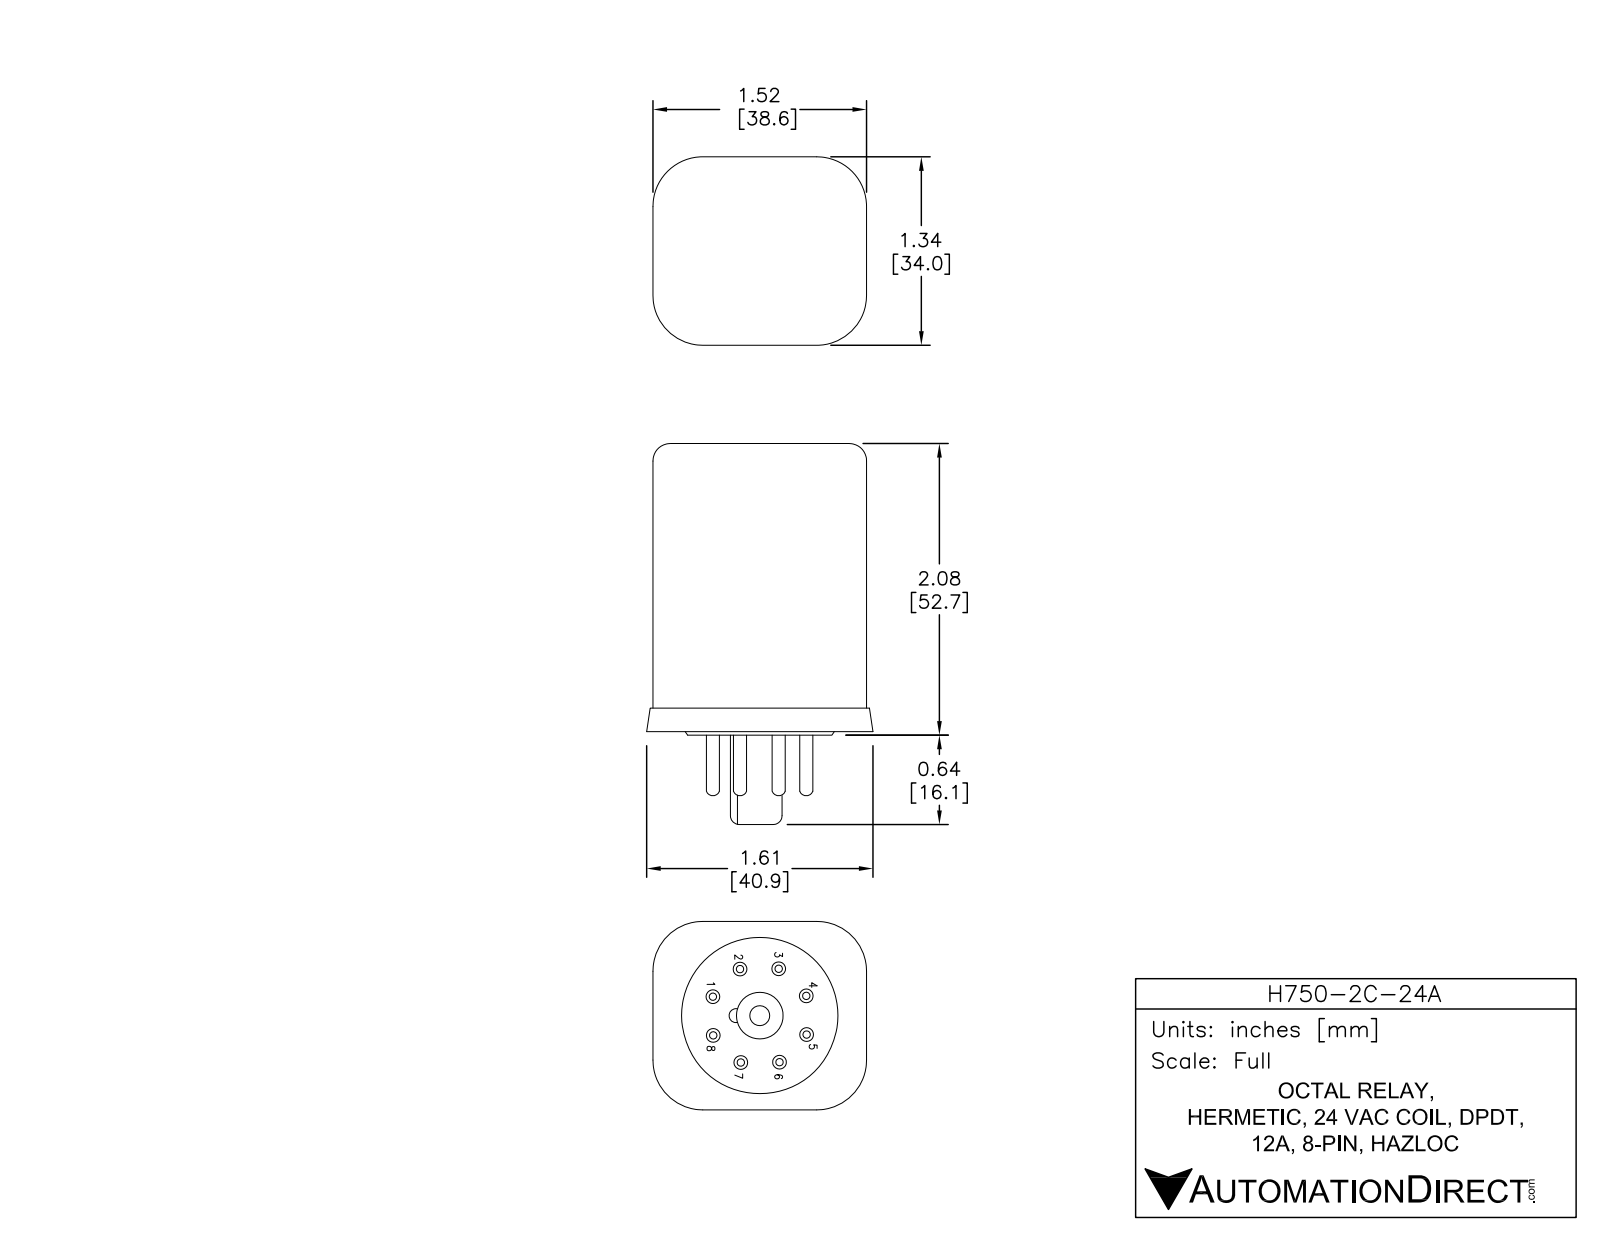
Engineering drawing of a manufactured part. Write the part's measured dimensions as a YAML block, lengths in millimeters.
part_name: "H750-2C-24A"
step_written_by: "SolidWorks 2013 (AUTOMOTIVE_DESIGN)"
units: millimeters
bodies: {solids: 1, faces: 271, planar: 123, cylindrical: 65, other: 83}
overall_size: [67.3, 41.35, 36.6]
volume: 66961
surface_area: 10714
round_holes:
  - {diameter: 4.5, count: 8}
  - {diameter: 3.9, count: 1}
round_bosses_or_shafts:
  - {diameter: 2.31, count: 8}
  - {diameter: 27, count: 1}
  - {diameter: 12, count: 1}
  - {diameter: 8, count: 1}
partial_cylinders:
  - {radius: 0.62, count: 8}
  - {radius: 2.5, count: 4}
  - {radius: 10, count: 4}
  - {radius: 11.3, count: 4}
  - {radius: 0.5, count: 2}
  - {radius: 0.59, count: 1}
face_to_face_distances: [53, 34, 38.75, 0.5, 53.5, 1.3, 35.3, 40.05, 1, 54]
hole_center_spacings: [8.5, 12.02, 15.7, 6.5, 6.51, 16.99]
